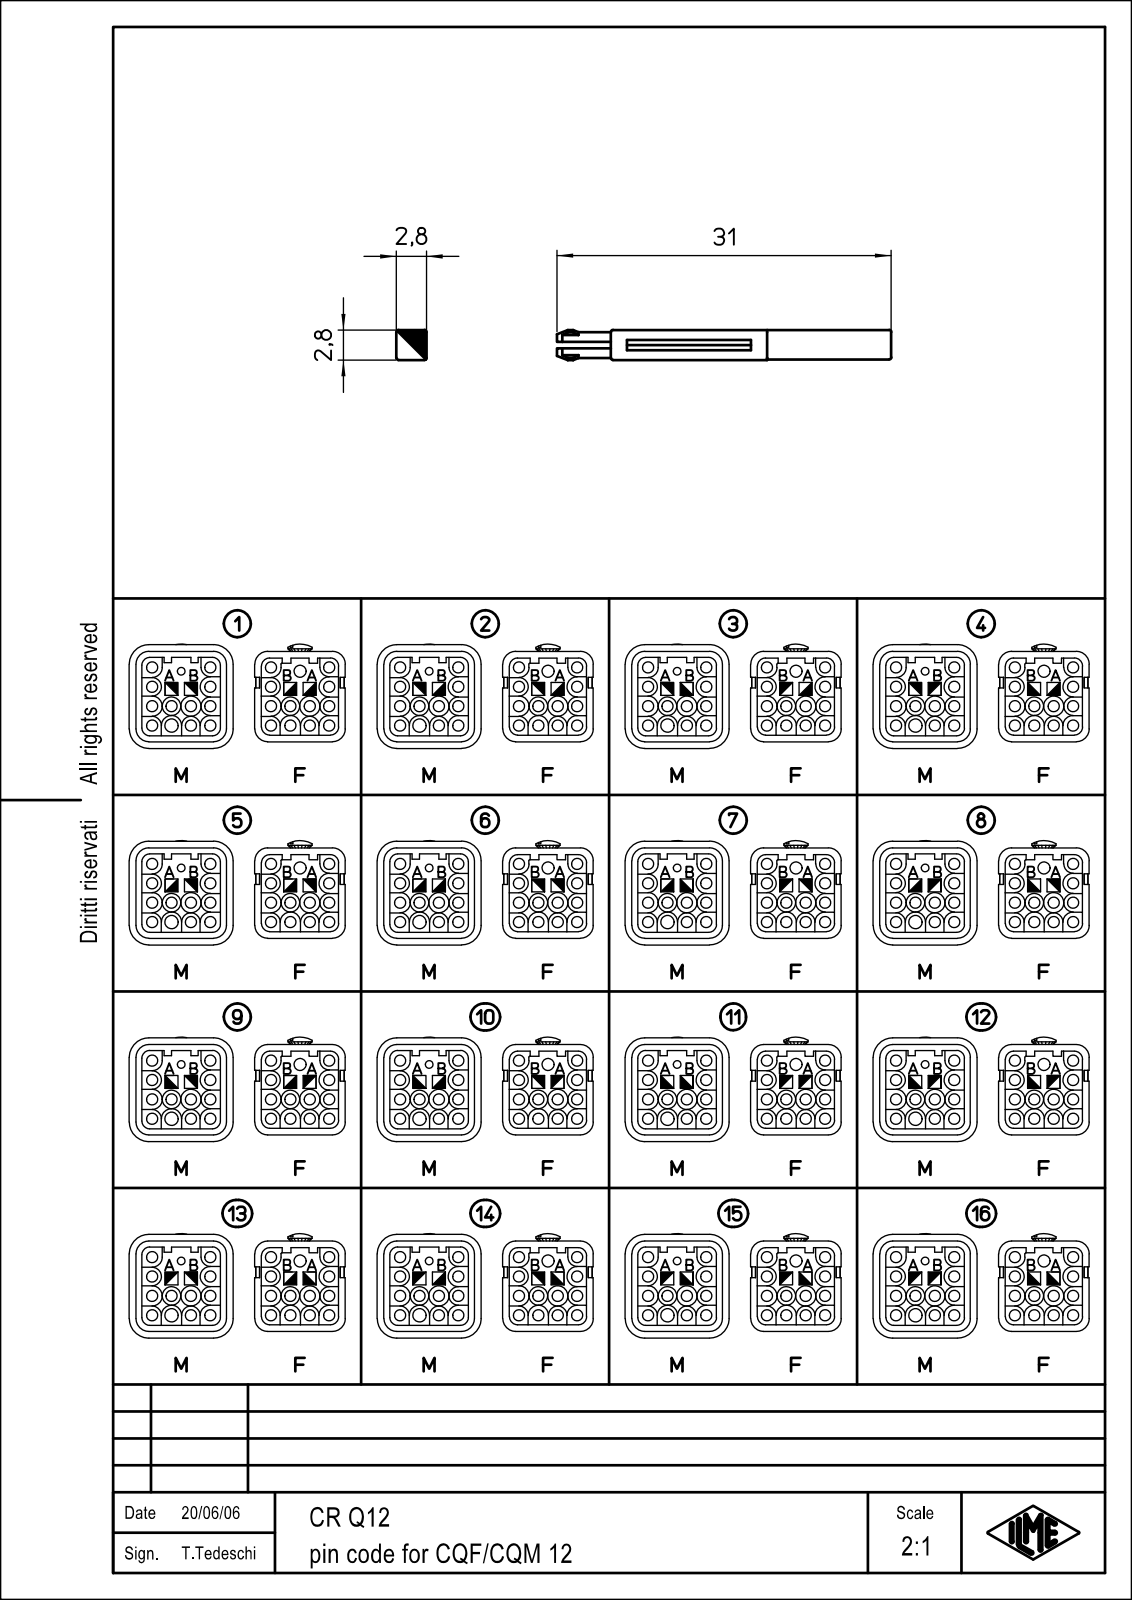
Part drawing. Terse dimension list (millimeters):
name: CR_Q12
written by: OneSpace Designer 13.20B 05-Dec-2005 (C) CoCreate Software GmbH (AUTOMOTIVE_DESIGN)
unit: mm
bodies: 1 solid, 37 faces (12 planar, 16 cylindrical, 9 other)
size: 30 × 2.8 × 2.8
volume: 174 mm³; area: 295 mm²
bosses: 1× ⌀2.4
rounds: 13× R0.2
face distances: 2.8, 20, 10, 30, 25, 15, 5
